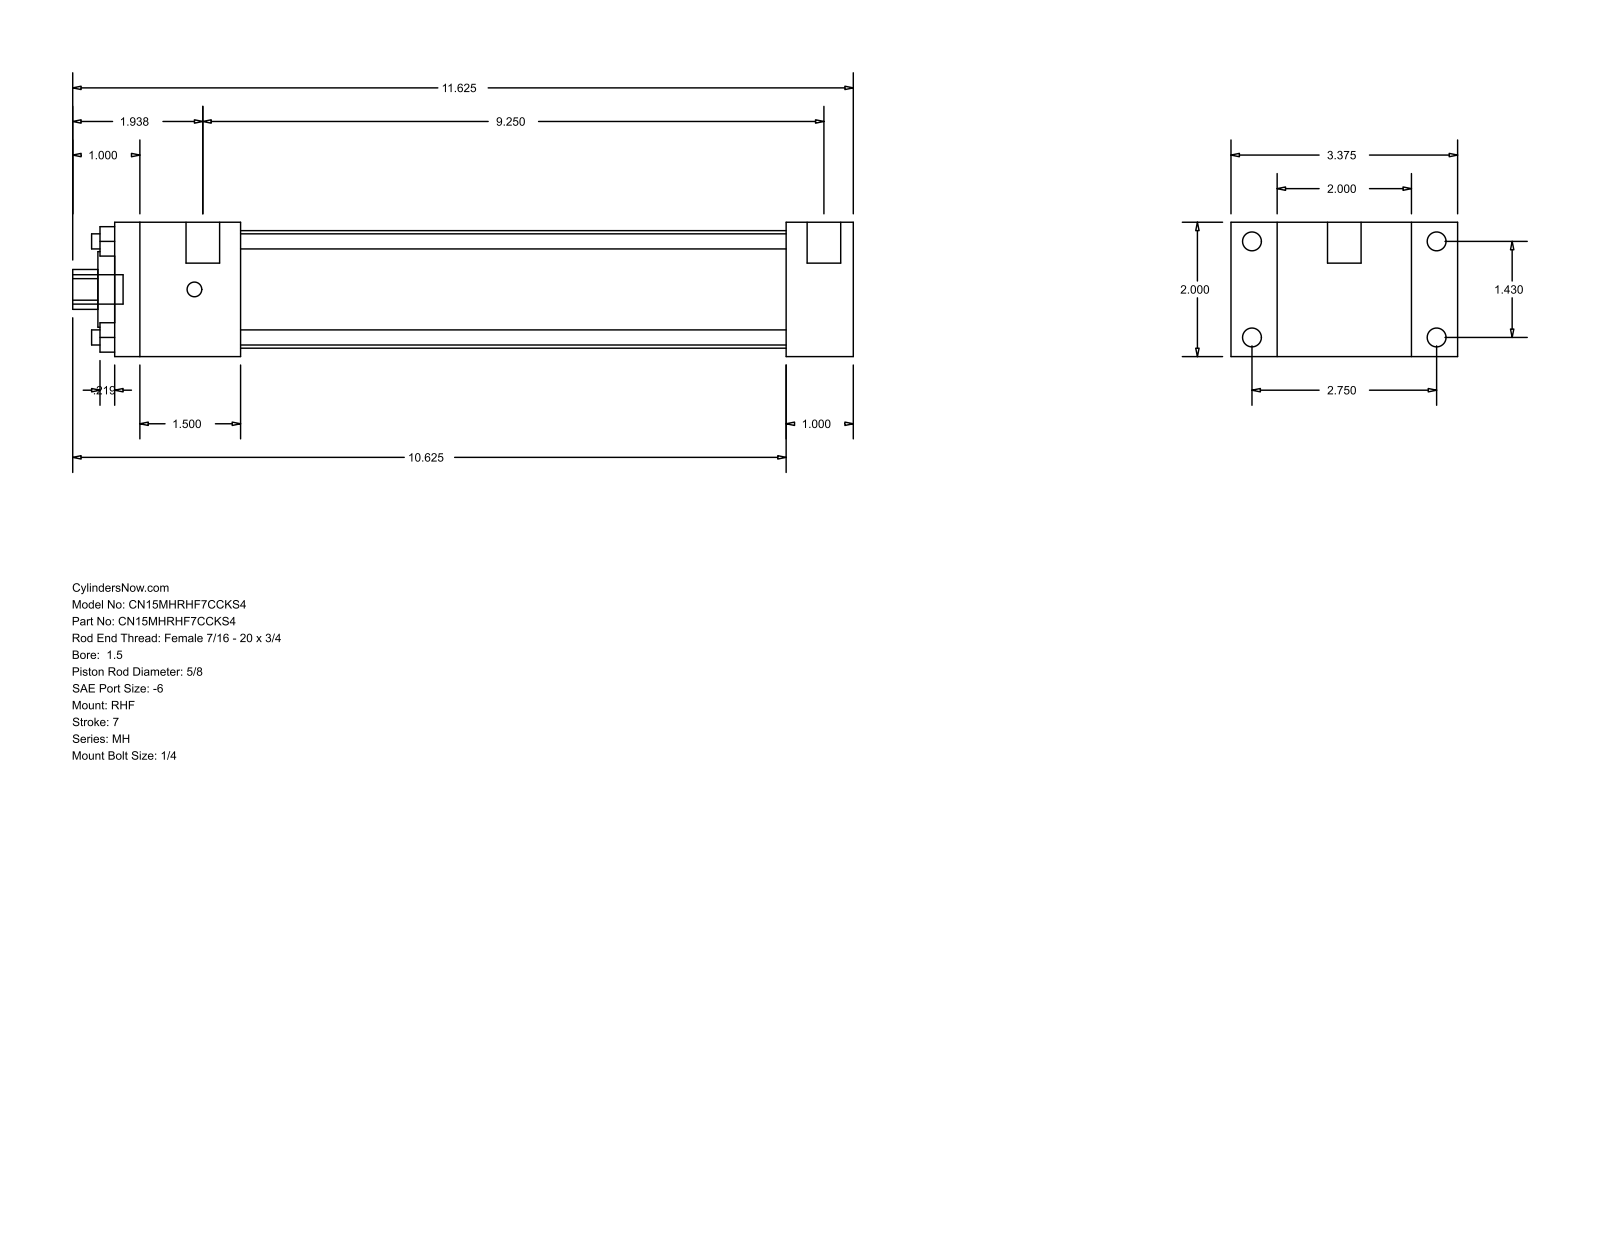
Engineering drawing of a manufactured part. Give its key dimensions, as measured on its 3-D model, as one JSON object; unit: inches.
{"part_name": "MH_RHF__0150_0.625", "step_written_by": "GSSL Pune (CONFIG_CONTROL_DESIGN)", "units": "inches", "bodies": {"solids": 0, "faces": 88, "planar": 60, "cylindrical": 28, "other": 0}, "overall_size": [11.625, 3.375, 2], "round_holes": [[0.225, 4], [0.625, 1], [1.125, 1], [1.75, 1]], "round_bosses_or_shafts": [[0.281, 4], [0.219, 4], [0.5, 2], [0.437, 1]], "partial_cylinders_radius": [[0.297, 1]], "face_to_face_distances": [2, 0.687, 2.687, 1, 10, 11, 3.375, 1.875, 8.125, 9.125], "hole_center_spacings": [1.011, 1.43, 2.022]}
